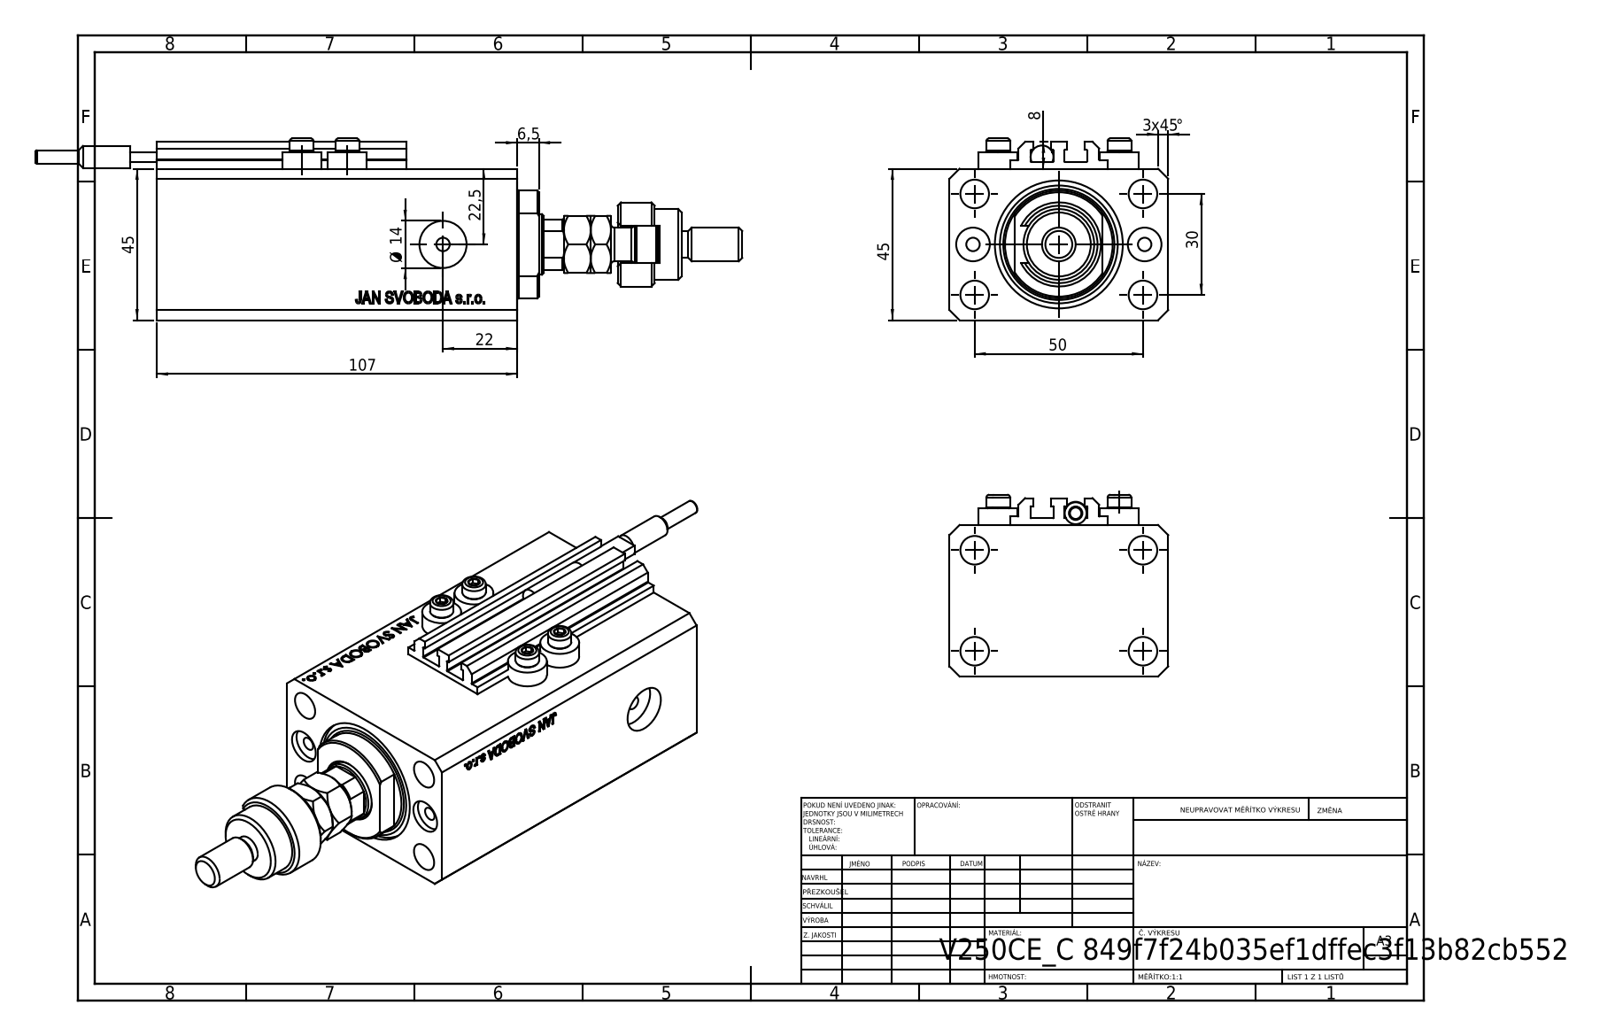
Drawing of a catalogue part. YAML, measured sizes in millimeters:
part_name: "MFA; FEMALE_PART_FOR_DFA; ALLEN BOLT V250CE; V250CE_C (+3 more)"
step_written_by: "SolidWorks 2019 (CONFIG_CONTROL_DESIGN)"
units: millimeters
bodies: {solids: 11, faces: 1144, planar: 547, cylindrical: 105, other: 492}
overall_size: [209.9, 65, 54]
volume: 302563
surface_area: 82914
round_holes:
  - {diameter: 4, count: 8}
  - {diameter: 8.5, count: 5}
  - {diameter: 10, count: 2}
  - {diameter: 14, count: 2}
  - {diameter: 18, count: 1}
  - {diameter: 38, count: 1}
round_bosses_or_shafts:
  - {diameter: 11.6, count: 4}
  - {diameter: 7, count: 4}
  - {diameter: 25, count: 1}
  - {diameter: 21, count: 1}
  - {diameter: 16, count: 1}
  - {diameter: 10, count: 1}
  - {diameter: 8, count: 1}
  - {diameter: 6.8, count: 1}
partial_cylinders:
  - {radius: 0.2, count: 10}
  - {radius: 5.5, count: 1}
  - {radius: 8.5, count: 1}
  - {radius: 8.75, count: 1}
  - {radius: 16, count: 1}
face_to_face_distances: [45, 65, 81.9, 25.1, 107, 47, 3, 2, 2.5, 75]
hole_center_spacings: [15.01, 29.15, 52.68, 13.6, 25.5, 30, 36, 38.48]
